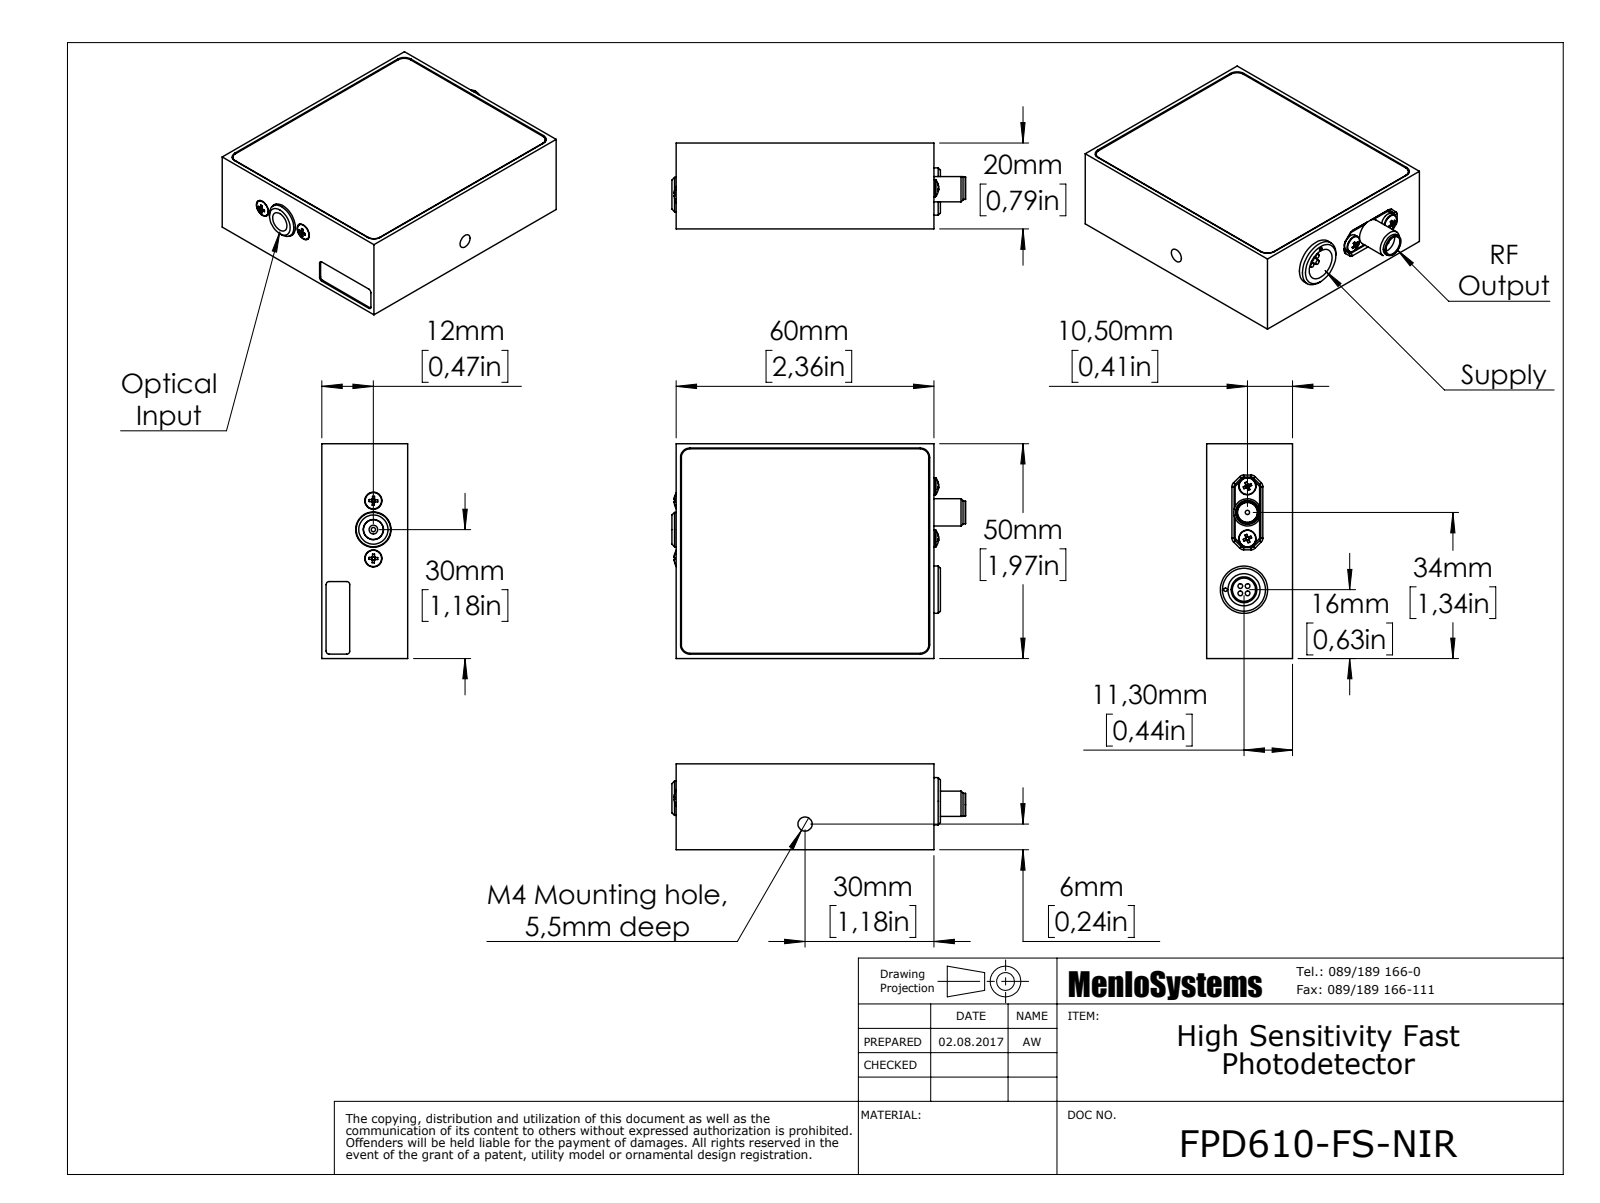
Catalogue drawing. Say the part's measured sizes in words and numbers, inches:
The part is named "FPD610-FS-NIR_170721". Its 3-D file was written by "SolidWorks 2016 (AUTOMOTIVE_DESIGN)". It is 22 solids with 1065 faces: 455 planar, 286 cylindrical and 324 other. Overall it measures 2.693 by 1.969 by 0.787 inches. Its volume is 2.351 cubic inches and its surface area 43.82 square inches. Round holes: 23 of diameter 0.063, 12 of diameter 0.157, 10 of diameter 0.087, 2 of diameter 0.102, 1 of diameter 0.031, 1 of diameter 0.039, 1 of diameter 0.08, 1 of diameter 0.126, 1 of diameter 0.13, 1 of diameter 0.181, 1 of diameter 0.185, 1 of diameter 0.295. Round bosses or shafts: 14 of diameter 0.079, 12 of diameter 0.15, 4 of diameter 0.043, 3 of diameter 0.02, 2 of diameter 0.157, 1 of diameter 0.433, 1 of diameter 0.378, 1 of diameter 0.354. Partial cylindrical surfaces (rounded edges, fillets, slot ends): 26 of radius 0.087, 8 of radius 0.028, 8 of radius 0.031, 8 of radius 0.079, 4 of radius 0.055, 2 of radius 0.059, 1 of radius 0.315. The main face-to-face distances are 0.059, 0.014, 0.77, 0.711, 0.073, 0.783, 0.256, 0.276, 1.969, 0.508. The hole center spacings are 0.166, 0.365, 0.413, 0.589, 0.65, 0.762, 0.787, 0.859.
